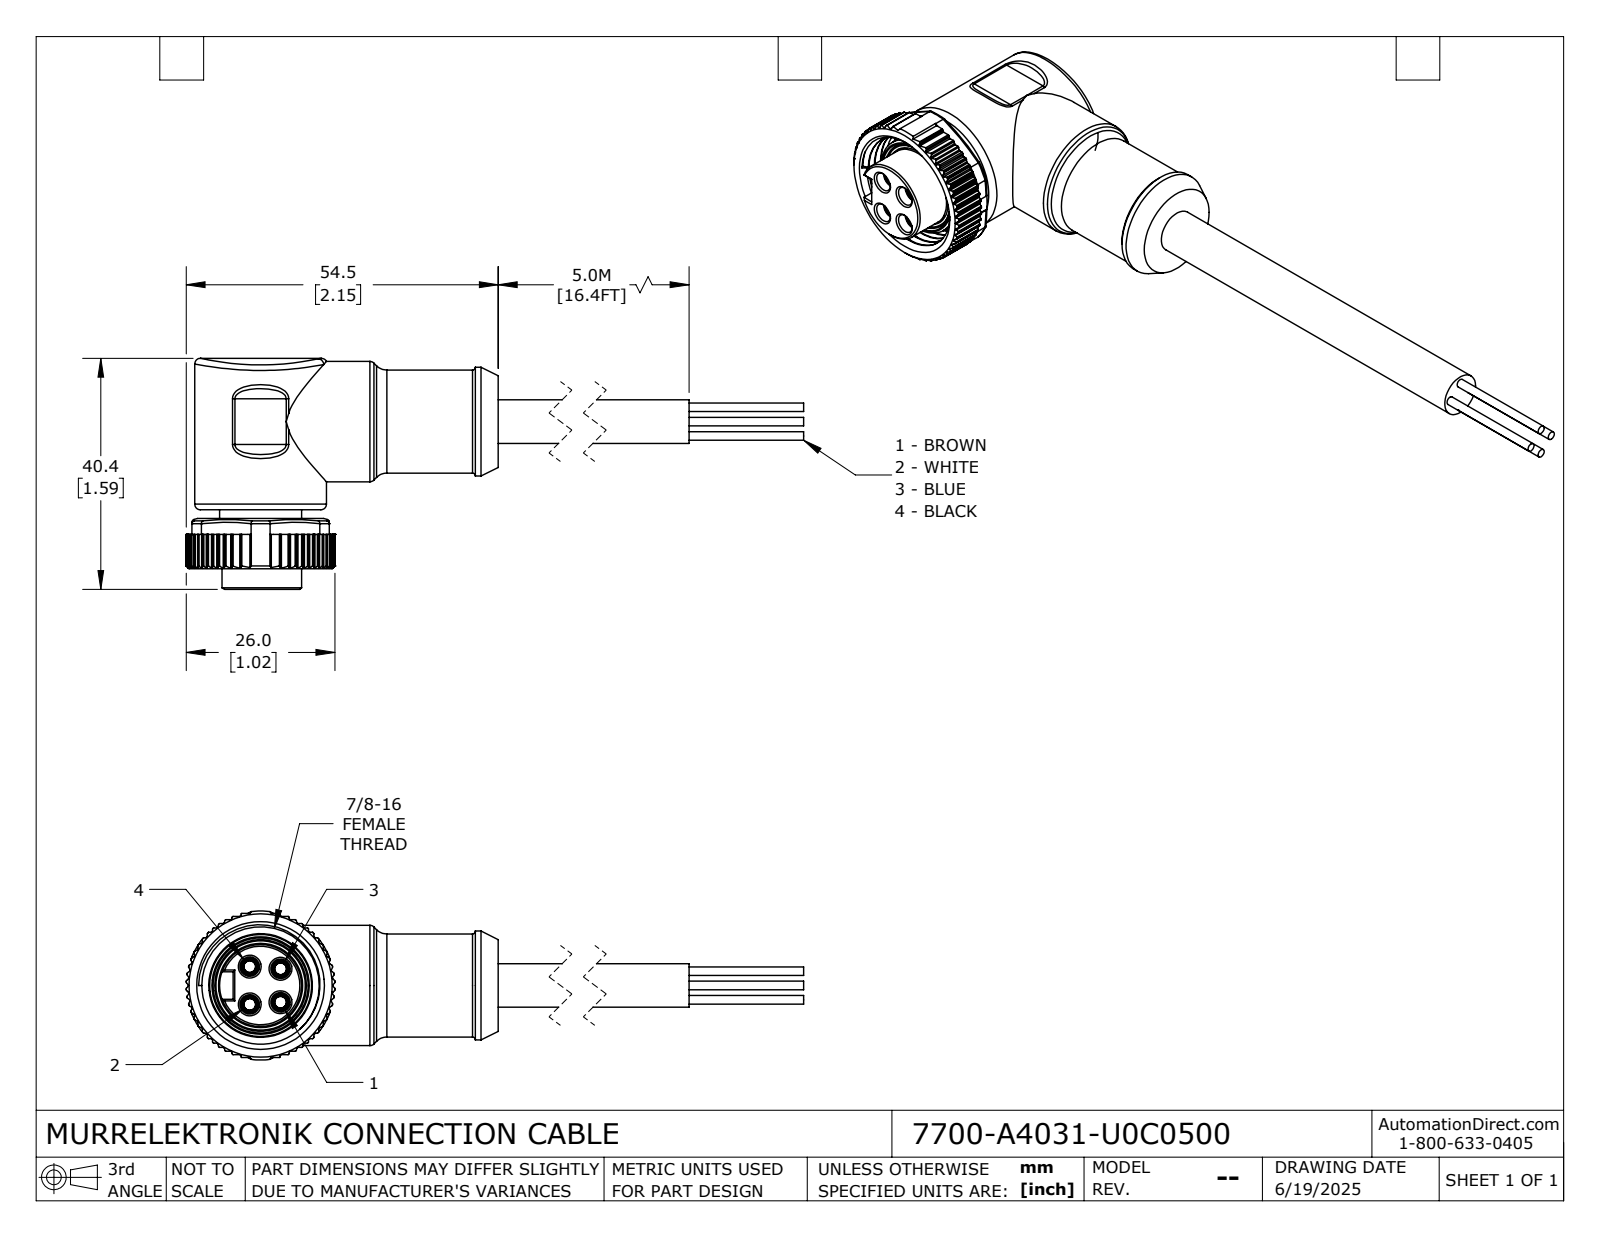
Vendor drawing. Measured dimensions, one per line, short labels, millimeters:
name: 7700-A4031-U0C0500
written by: SolidWorks 2024 (CONFIG_CONTROL_DESIGN)
unit: mm
bodies: 1 solid, 700 faces (294 planar, 315 cylindrical, 91 other)
size: 144.49 × 40.36 × 26
volume: 26 793 mm³; area: 9 847 mm²
holes: 4× ⌀2.05, 4× ⌀3, 4× ⌀3.4, 1× ⌀15.5, 1× ⌀15.6, 1× ⌀20.5, 1× ⌀22.23
bosses: 4× ⌀1.5, 1× ⌀23, 1× ⌀21, 1× ⌀19, 1× ⌀18.1, 1× ⌀18, 1× ⌀17.8, 1× ⌀14.3
rounds: 126× R0.2, 16× R0.3, 4× R0.1, 4× R0.73, 4× R1, 4× R2.5, 1× R13, 1× R50
face distances: 1.5, 3.6, 8.8, 10.3, 12.4, 13.9, 7.3, 3, 10.9, 21
hole spacings: 3.81, 4.54, 5.39, 8.22, 5.84, 6.6
